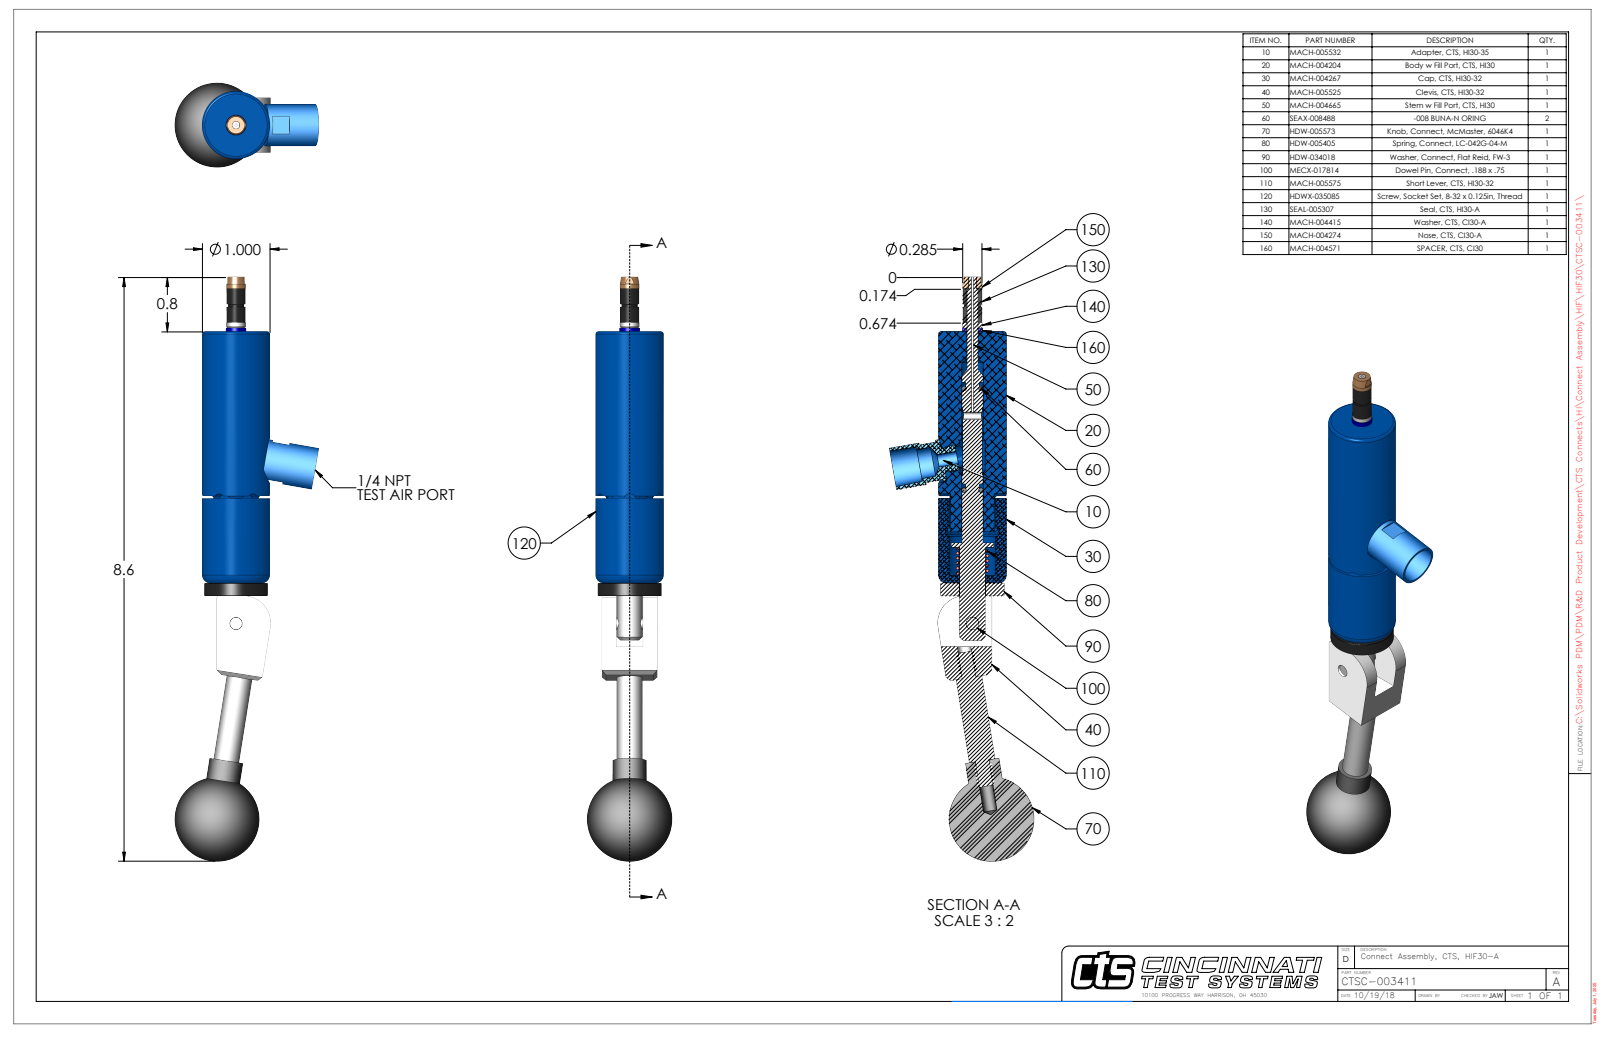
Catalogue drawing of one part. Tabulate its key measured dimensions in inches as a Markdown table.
| quantity | value |
| --- | --- |
| part name | CTSC-003411 |
| STEP written by | SolidWorks 2023 (AUTOMOTIVE_DESIGN) |
| units | inches |
| bodies | 11 solids, 290 faces (102 planar, 124 cylindrical, 64 other) |
| overall size | 8.63 × 2.128 × 1.25 |
| volume | 4.917 in³ |
| surface area | 36.08 in² |
| round holes (diameter × count) | 0.201 × 2, 0.04 × 1, 0.1 × 1, 0.113 × 1, 0.136 × 1, 0.15 × 1, 0.155 × 1, 0.161 × 1, 0.164 × 1, 0.187 × 1, 0.189 × 1, 0.385 × 1 |
| round bosses / shafts (diameter × count) | 1 × 1, 0.936 × 1, 0.62 × 1, 0.5 × 1, 0.38 × 1, 0.375 × 1, 0.3 × 1, 0.288 × 1 |
| partial cylindrical surfaces (radius × count) | 0.093 × 6, 0.015 × 1, 0.054 × 1, 0.325 × 1, 0.4 × 1, 0.443 × 1, 0.475 × 1 |
| main face-to-face distances | 0.21, 0.602, 0.812, 0.187, 3.717, 3.904, 0.391, 2.463, 1.253, 1.441 |
| hole center spacings | 0.599, 1.658, 2.252 |
